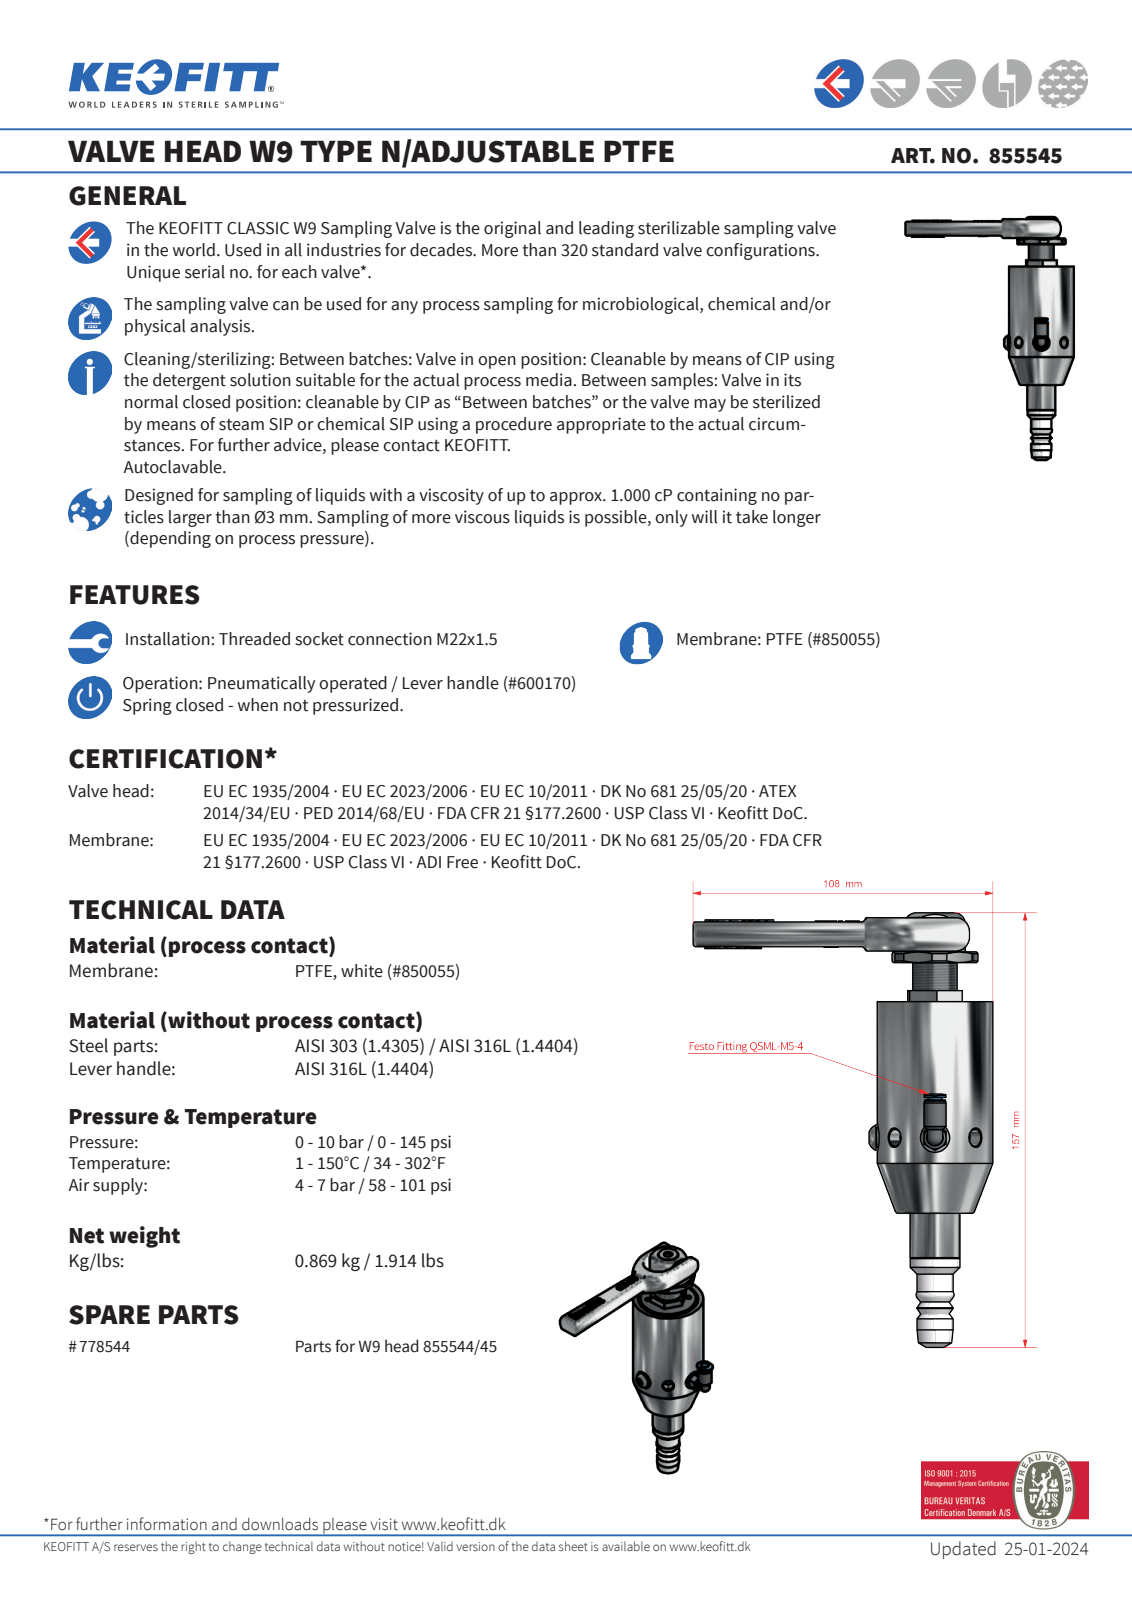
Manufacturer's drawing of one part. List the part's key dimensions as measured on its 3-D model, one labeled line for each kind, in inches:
Part name (STEP PRODUCT): 855545
STEP written by: Autodesk Inventor 2020 (AUTOMOTIVE_DESIGN)
Units: inches
Bodies: 1 solid, 333 faces (132 planar, 106 cylindrical, 95 other)
Overall size (bounding box): 6.161 × 2.222 × 1.754
Volume: 6.604 in³ · Surface area: 53.22 in²
Round holes (diameter × count): ⌀0.157 ×3, ⌀0.067 ×2, ⌀0.118 ×2, ⌀0.165 ×2, ⌀0.199 ×2, ⌀0.238 ×2, ⌀0.413 ×2, ⌀0.315 ×1, ⌀0.398 ×1, ⌀0.402 ×1, ⌀0.453 ×1, ⌀0.472 ×1
Round bosses / shafts (diameter × count): ⌀0.197 ×3, ⌀0.291 ×2, ⌀0.246 ×2, ⌀0.22 ×2, ⌀1.638 ×1, ⌀1.339 ×1, ⌀1.28 ×1, ⌀1.26 ×1
Partial cylindrical surfaces — rounded edges, fillets, slot ends (radius × count): R0.02 ×12, R0.02 ×4, R0.118 ×4, R0.059 ×2, R0.154 ×2, R0.087 ×1, R0.429 ×1
Main face-to-face distances: 0.709, 0.551, 0.157, 0.039, 1.693, 3.551, 3, 3.709, 2.244, 0.079
Hole centre spacings: 0.472, 0.945, 0.978, 1.211, 1.556
